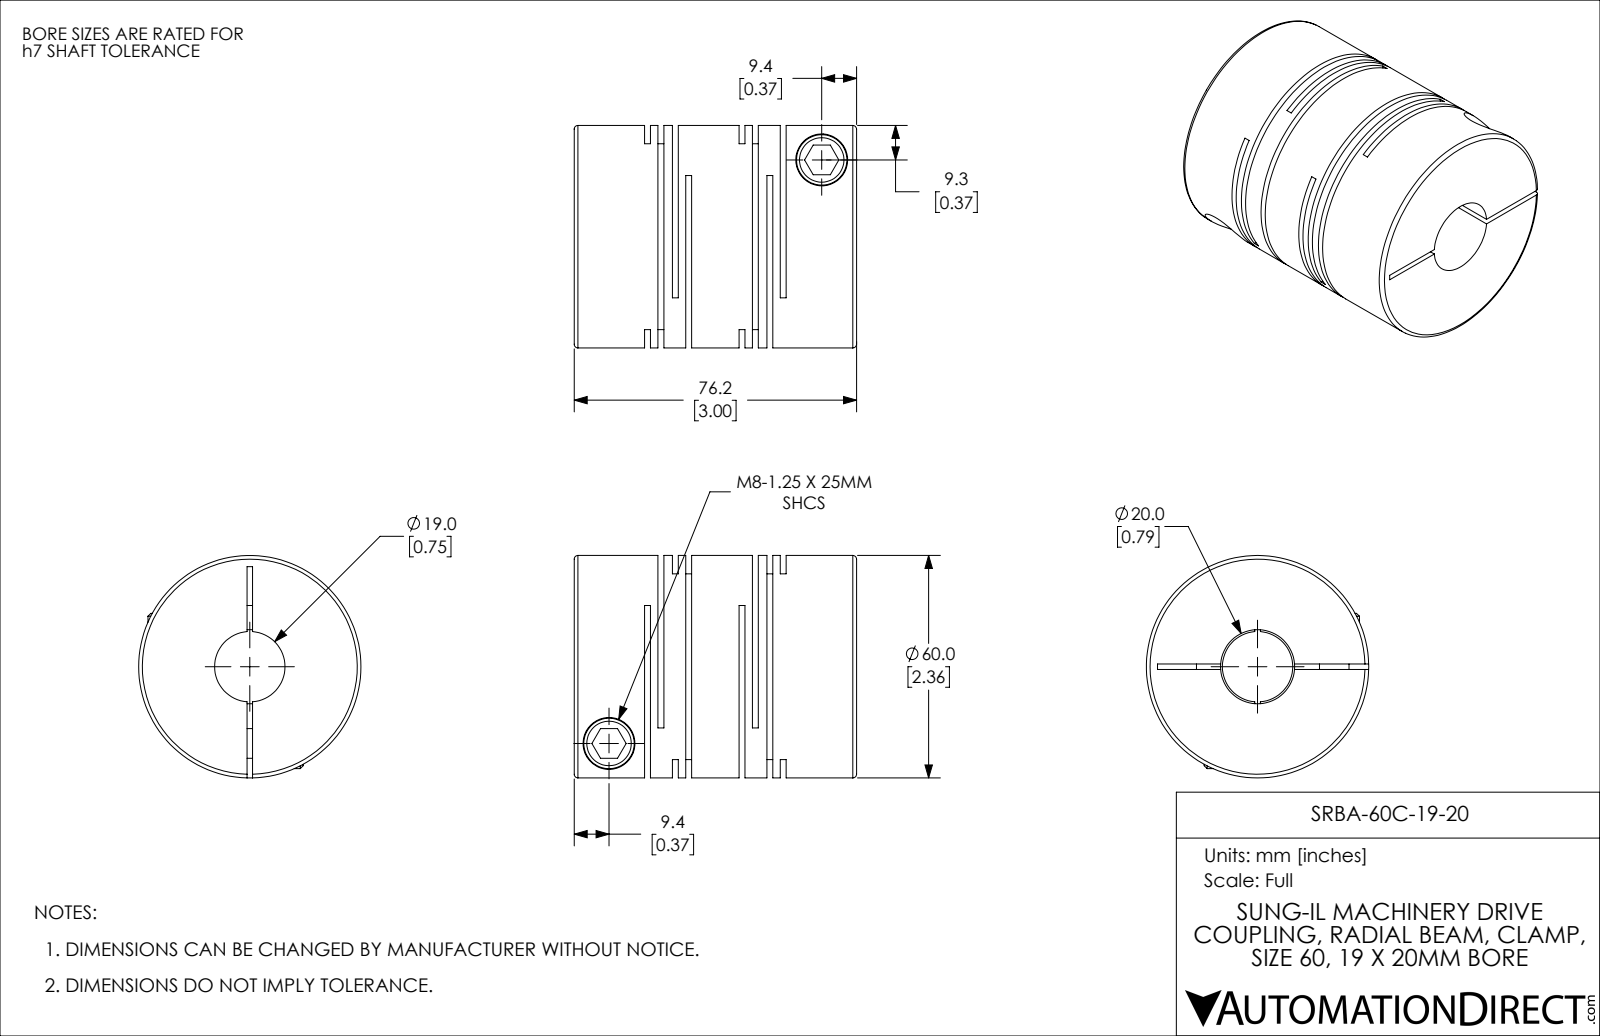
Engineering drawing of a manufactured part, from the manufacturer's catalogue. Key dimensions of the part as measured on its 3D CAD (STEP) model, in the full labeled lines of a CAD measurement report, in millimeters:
Part name (STEP PRODUCT): SRBA-60C-19-20
STEP written by: SolidWorks 2021 (CONFIG_CONTROL_DESIGN)
Units: millimetres
Bodies: 1 solid, 115 faces (60 planar, 42 cylindrical, 13 other)
Overall size (bounding box): 76.2 × 60 × 60
Volume: 160 800 mm³ · Surface area: 59 160 mm²
Round holes (diameter × count): ⌀8 ×2, ⌀14 ×2, ⌀19 ×1, ⌀20 ×1
Round bosses / shafts (diameter × count): ⌀13.6 ×2, ⌀60 ×1
Main face-to-face distances: 1.6, 3.6, 7.5, 25.5, 33, 27.1, 5.9, 23.9, 18, 2
